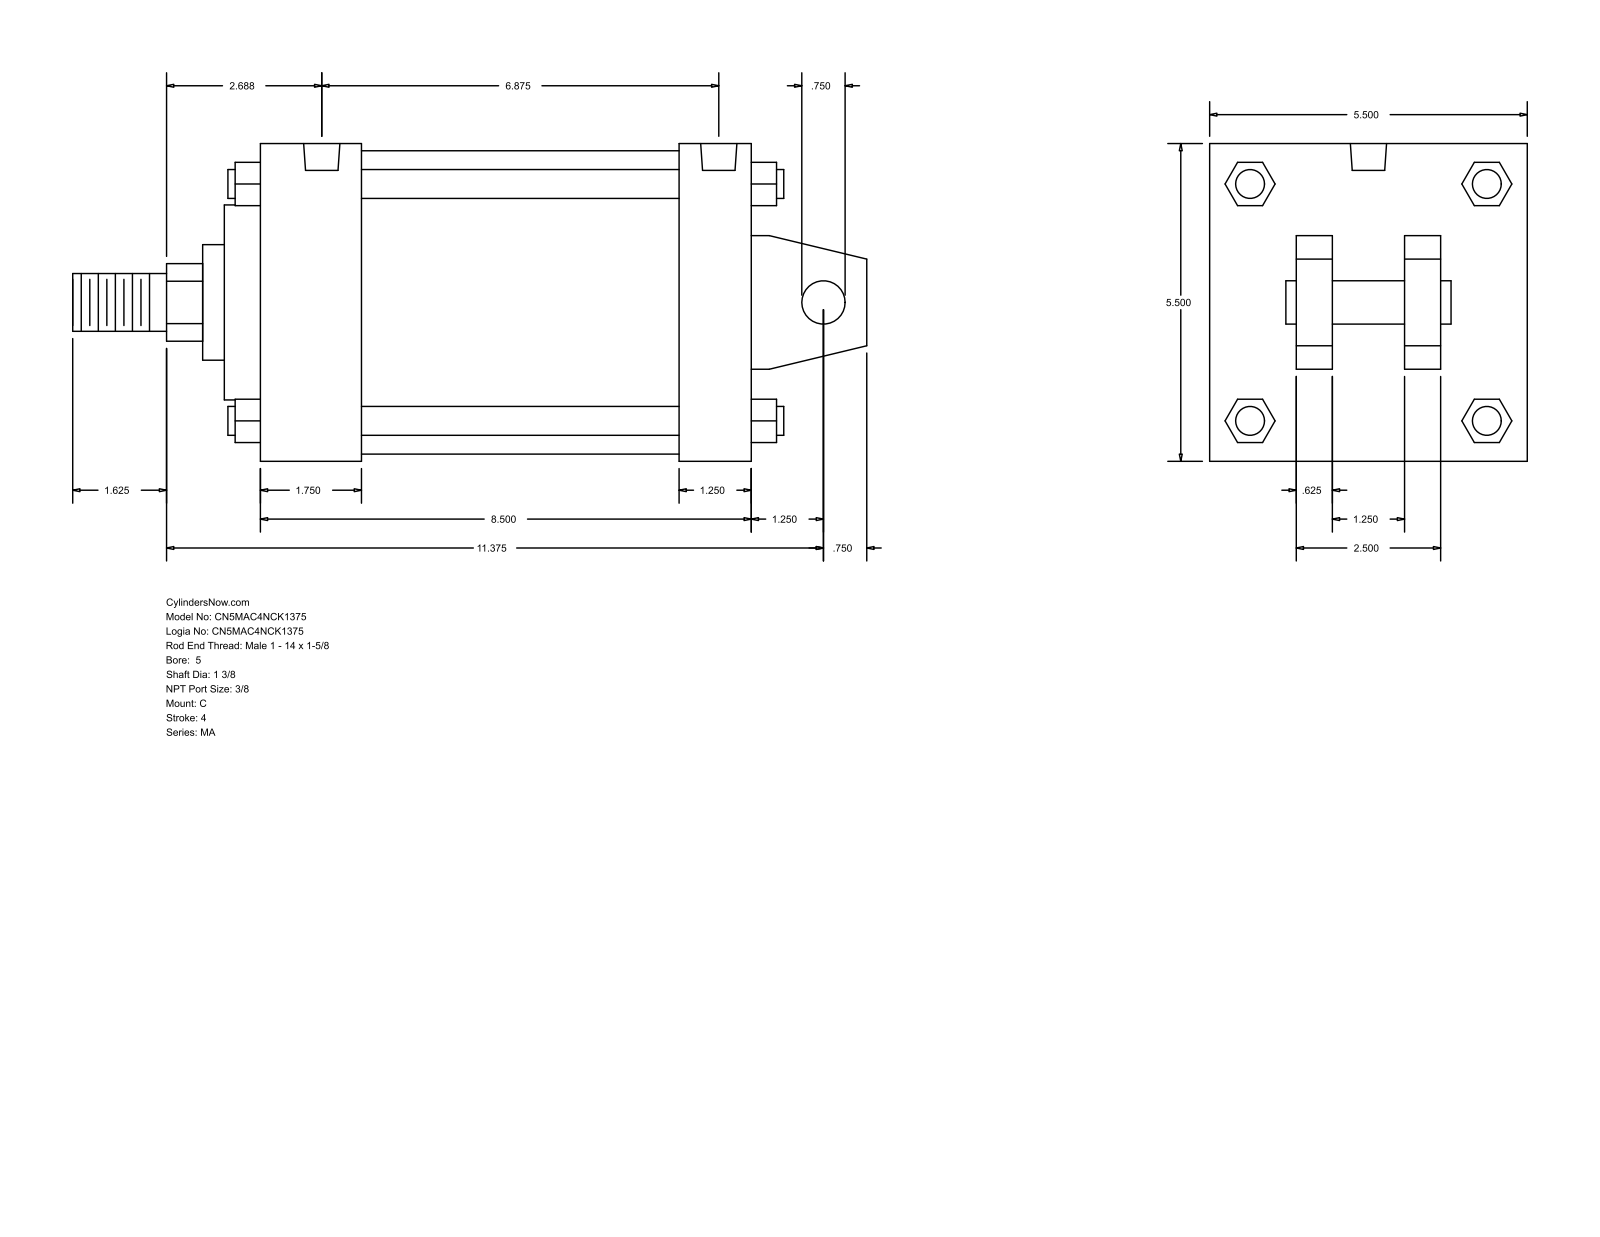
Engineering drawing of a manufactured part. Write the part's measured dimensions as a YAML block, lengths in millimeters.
part_name: "MA_C__0500_1.375"
step_written_by: "GSSL Pune (CONFIG_CONTROL_DESIGN)"
units: millimeters
bodies: {solids: 0, faces: 141, planar: 109, cylindrical: 32, other: 0}
overall_size: [349.25, 139.7, 139.7]
round_holes:
  - {diameter: 11.11, count: 4}
  - {diameter: 15.93, count: 2}
round_bosses_or_shafts:
  - {diameter: 12.7, count: 4}
  - {diameter: 133.35, count: 1}
  - {diameter: 85.72, count: 1}
  - {diameter: 50.8, count: 1}
  - {diameter: 34.92, count: 1}
  - {diameter: 25.4, count: 1}
  - {diameter: 19.05, count: 1}
partial_cylinders:
  - {radius: 17.06, count: 1}
face_to_face_distances: [139.7, 215.91, 15.87, 184.16, 31.75, 44.45, 139.71, 171.46, 53.97, 38.1]
hole_center_spacings: [4.77, 165.09, 169.86, 174.63]
